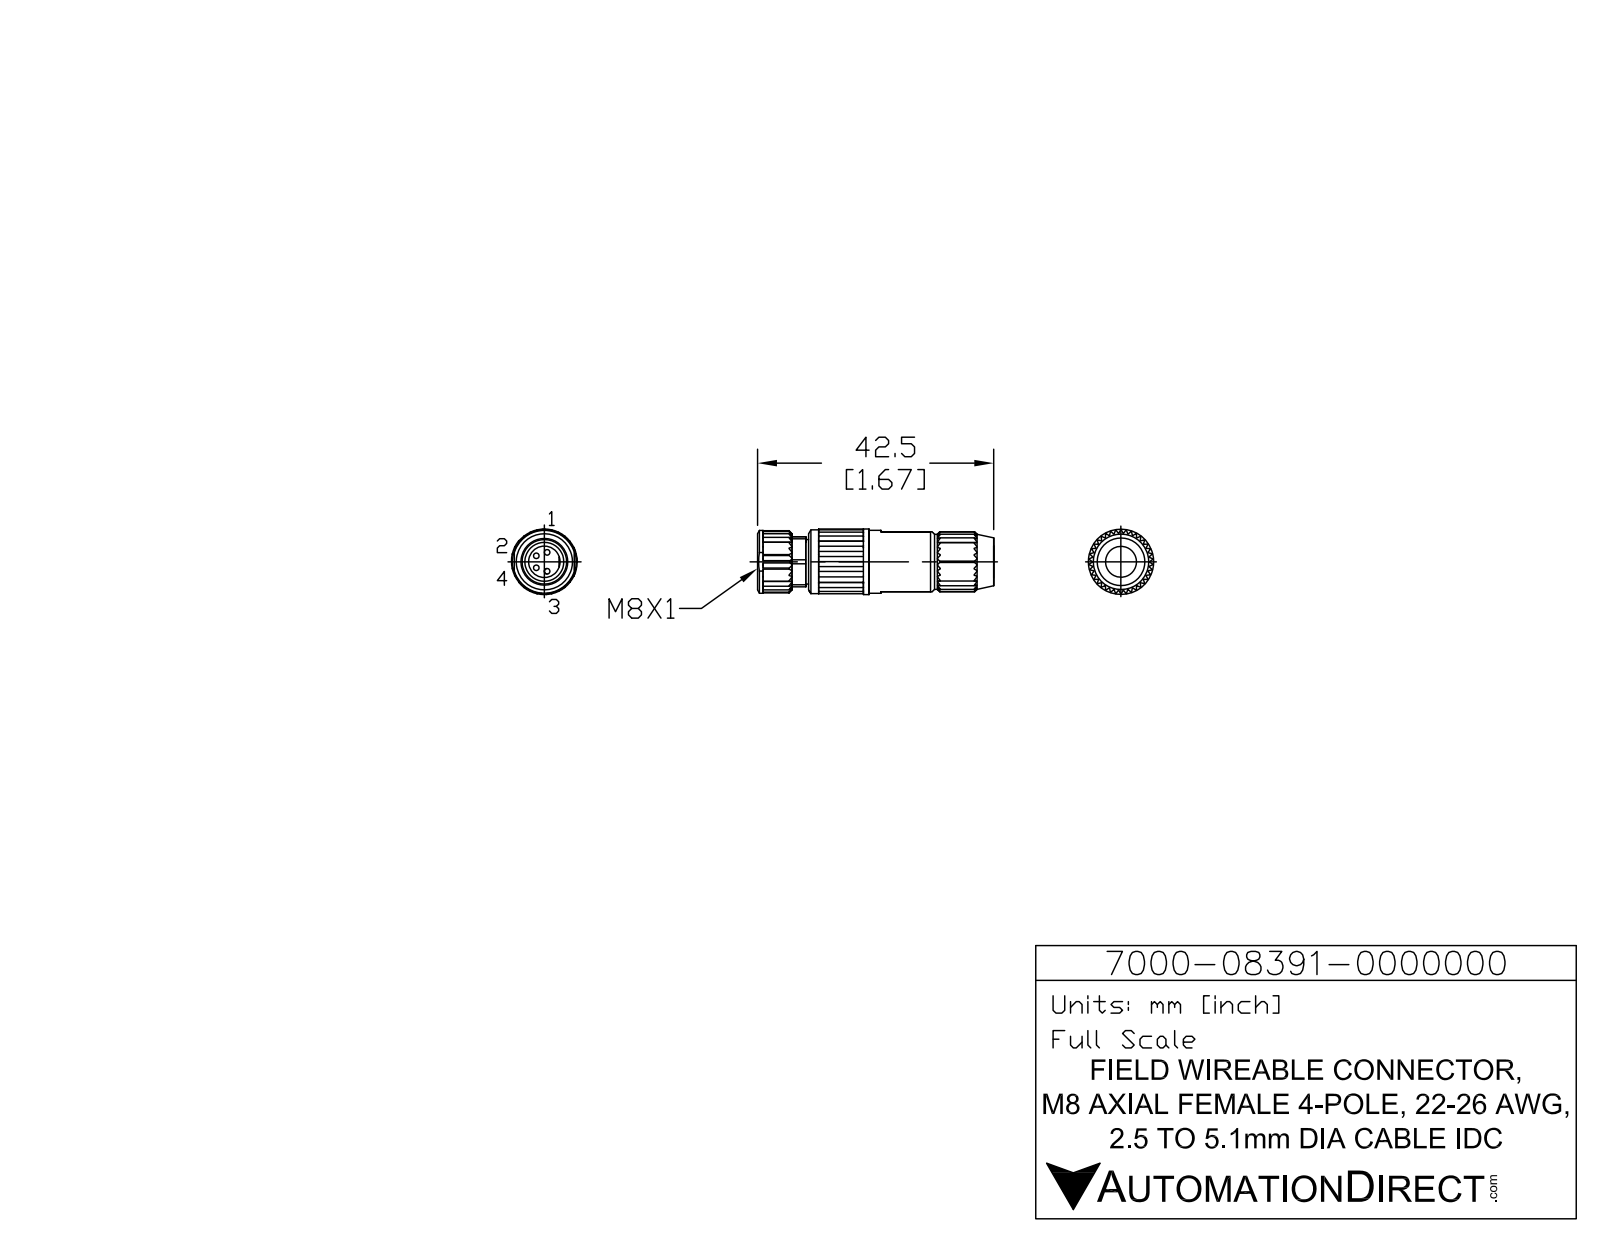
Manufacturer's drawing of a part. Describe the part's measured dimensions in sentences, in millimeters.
The part is named "7000-08391-0000000". Its 3-D file was written by "SolidWorks 2015 (AUTOMOTIVE_DESIGN)". It is 1 solid with 396 faces: 322 planar, 22 cylindrical and 52 other. Overall it measures 42.5 by 11.8 by 11.8 millimeters. Its volume is 3 639 cubic millimeters and its surface area 3 151 square millimeters. Round holes: 4 of diameter 1, 1 of diameter 5.58, 1 of diameter 6.76. Round bosses or shafts: 1 of diameter 11.8, 1 of diameter 11.74, 1 of diameter 10, 1 of diameter 5.7. The main face-to-face distances are 5.6, 5.58, 8.9, 42.5, 33.8, 8.7, 12.9, 1.66, 7.24, 10.5. The hole center spacings are 1.7, 1.75, 2.92, 1.6, 3.4.
